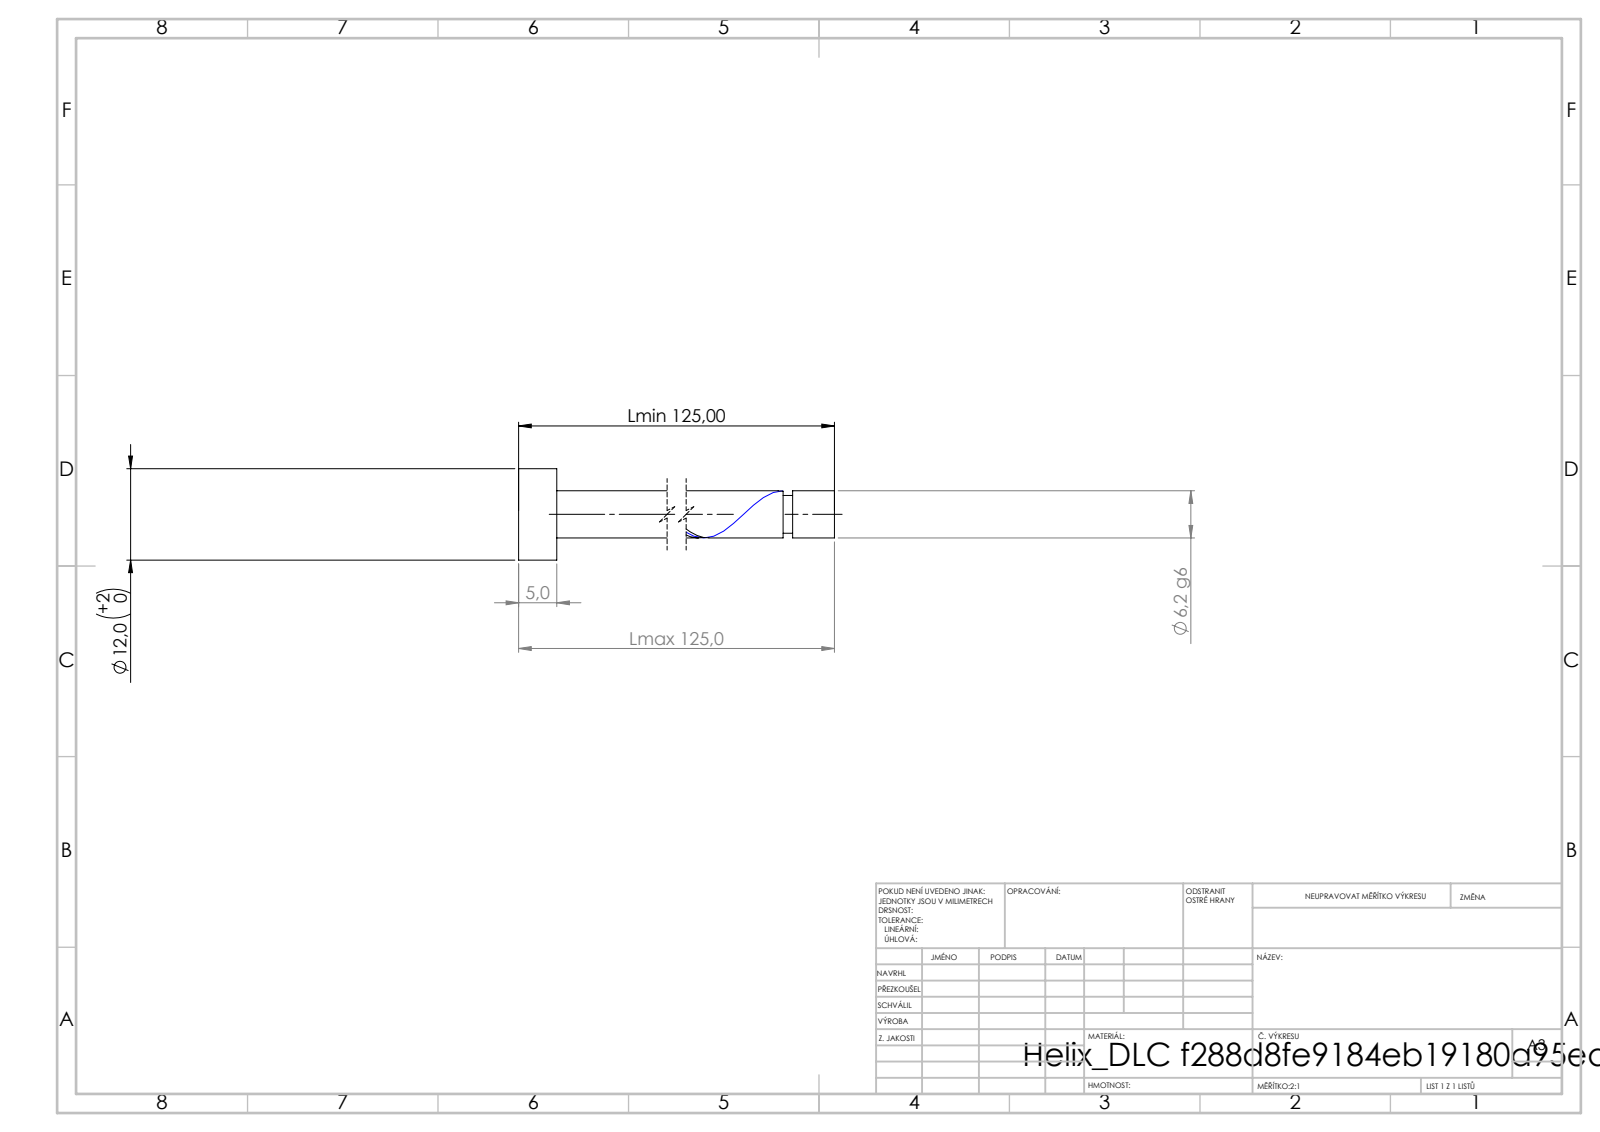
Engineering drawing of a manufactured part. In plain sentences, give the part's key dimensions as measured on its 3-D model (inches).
Its 3-D file was written by "SolidWorks 2019 (CONFIG_CONTROL_DESIGN)". It is 1 solid with 21 faces: 6 planar, 14 cylindrical and 1 other. Overall it measures 4.921 by 0.472 by 0.472 inches. Its volume is 0.253 cubic inches and its surface area 4.38 square inches. Round bosses or shafts: 1 of diameter 0.472, 1 of diameter 0.244, 1 of diameter 0.195. The main face-to-face distances are 0.197, 4.921, 4.724, 4.705, 4.508, 0.216, 4.656, 4.459, 0.049, 0.265.
